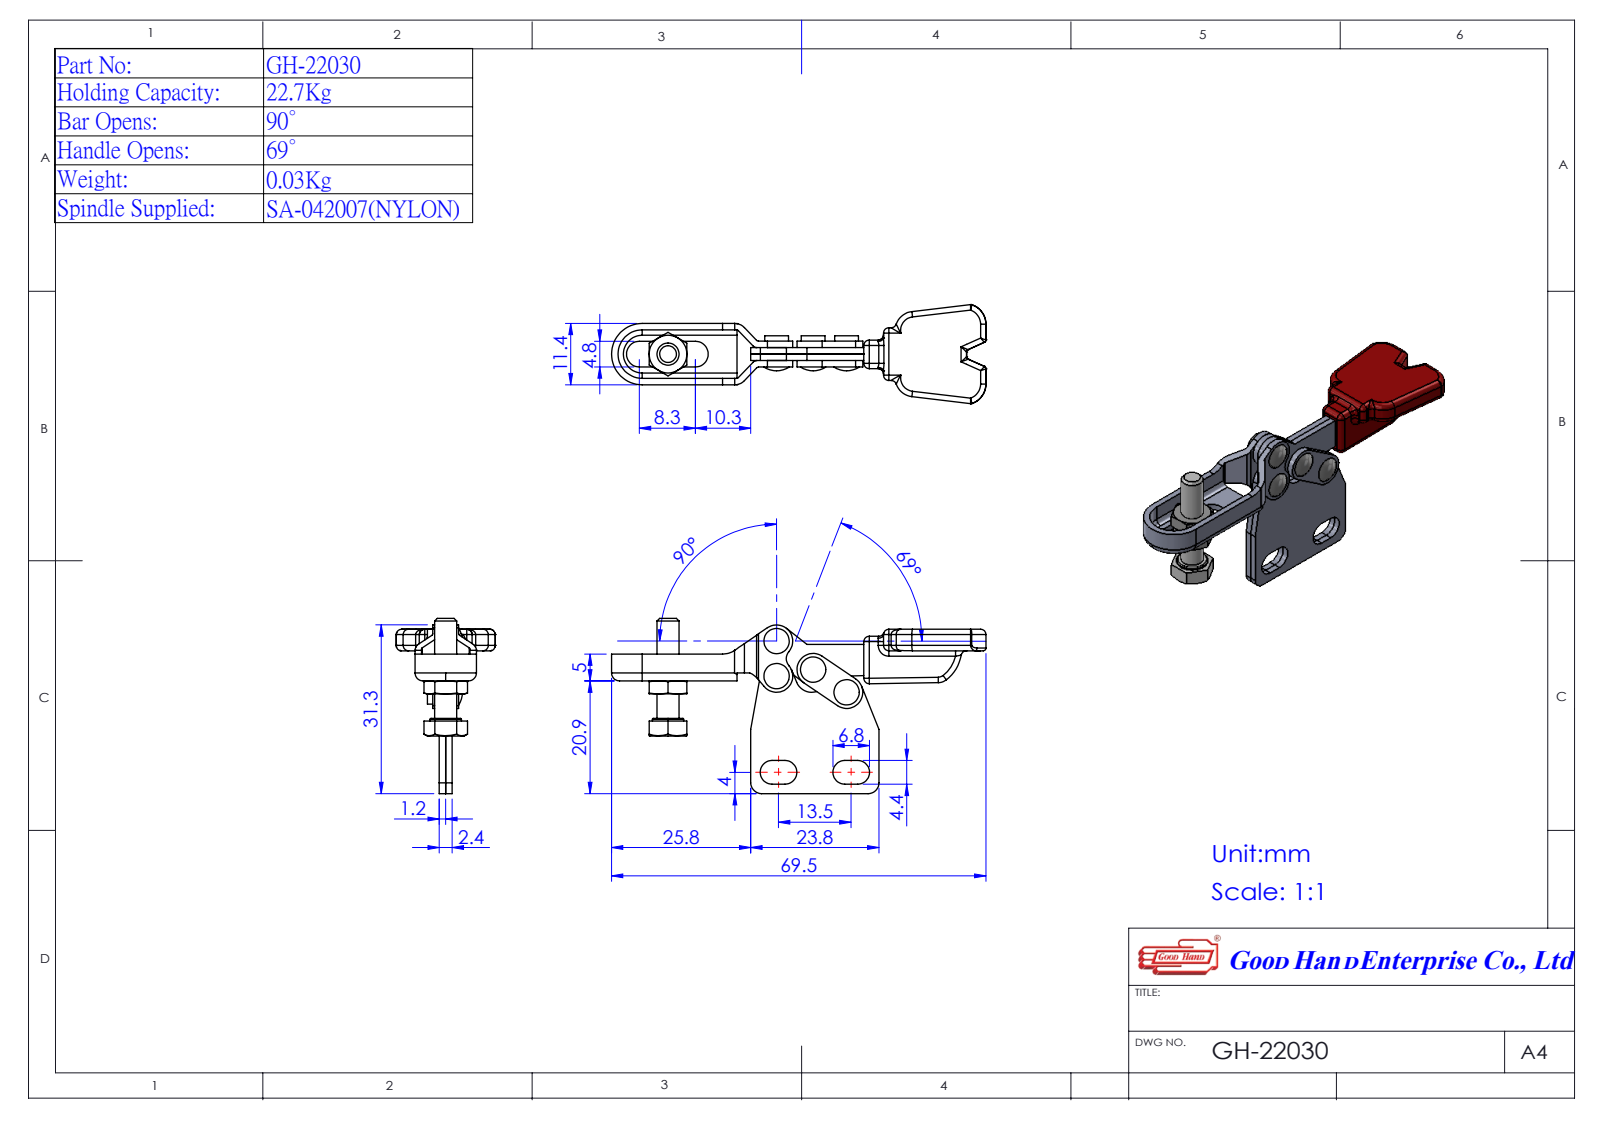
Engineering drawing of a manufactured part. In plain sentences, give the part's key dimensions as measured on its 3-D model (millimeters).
The part is named "12201014(簡化); Group3^GH-22030(簡化); Group2^GH-22030(簡化); 12200501-1^GH-22030(簡化) (+2 more)". Its 3-D file was written by "SolidWorks 2016 (AUTOMOTIVE_DESIGN)". It is 6 solids with 306 faces: 128 planar, 130 cylindrical and 48 other. Overall it measures 69.5 by 34 by 18.39 millimeters. Its volume is 4 547 cubic millimeters and its surface area 6 189 square millimeters. Round holes: 4 of diameter 2. Round bosses or shafts: 4 of diameter 3.5, 1 of diameter 6, 1 of diameter 5.8, 1 of diameter 4.1. Partial cylindrical surfaces (rounded edges, fillets, slot ends): 20 of radius 1, 5 of radius 0.5, 5 of radius 3, 4 of radius 2, 4 of radius 2.2, 3 of radius 2.5, 2 of radius 2.38, 2 of radius 3.5. The main face-to-face distances are 1.2, 2.4, 4.5, 6.9, 3.3, 5.7, 8.4, 3.6, 9.6, 5.6. The hole center spacings are 6.5, 6.91, 7.49, 8.62, 13.34, 16.1.
